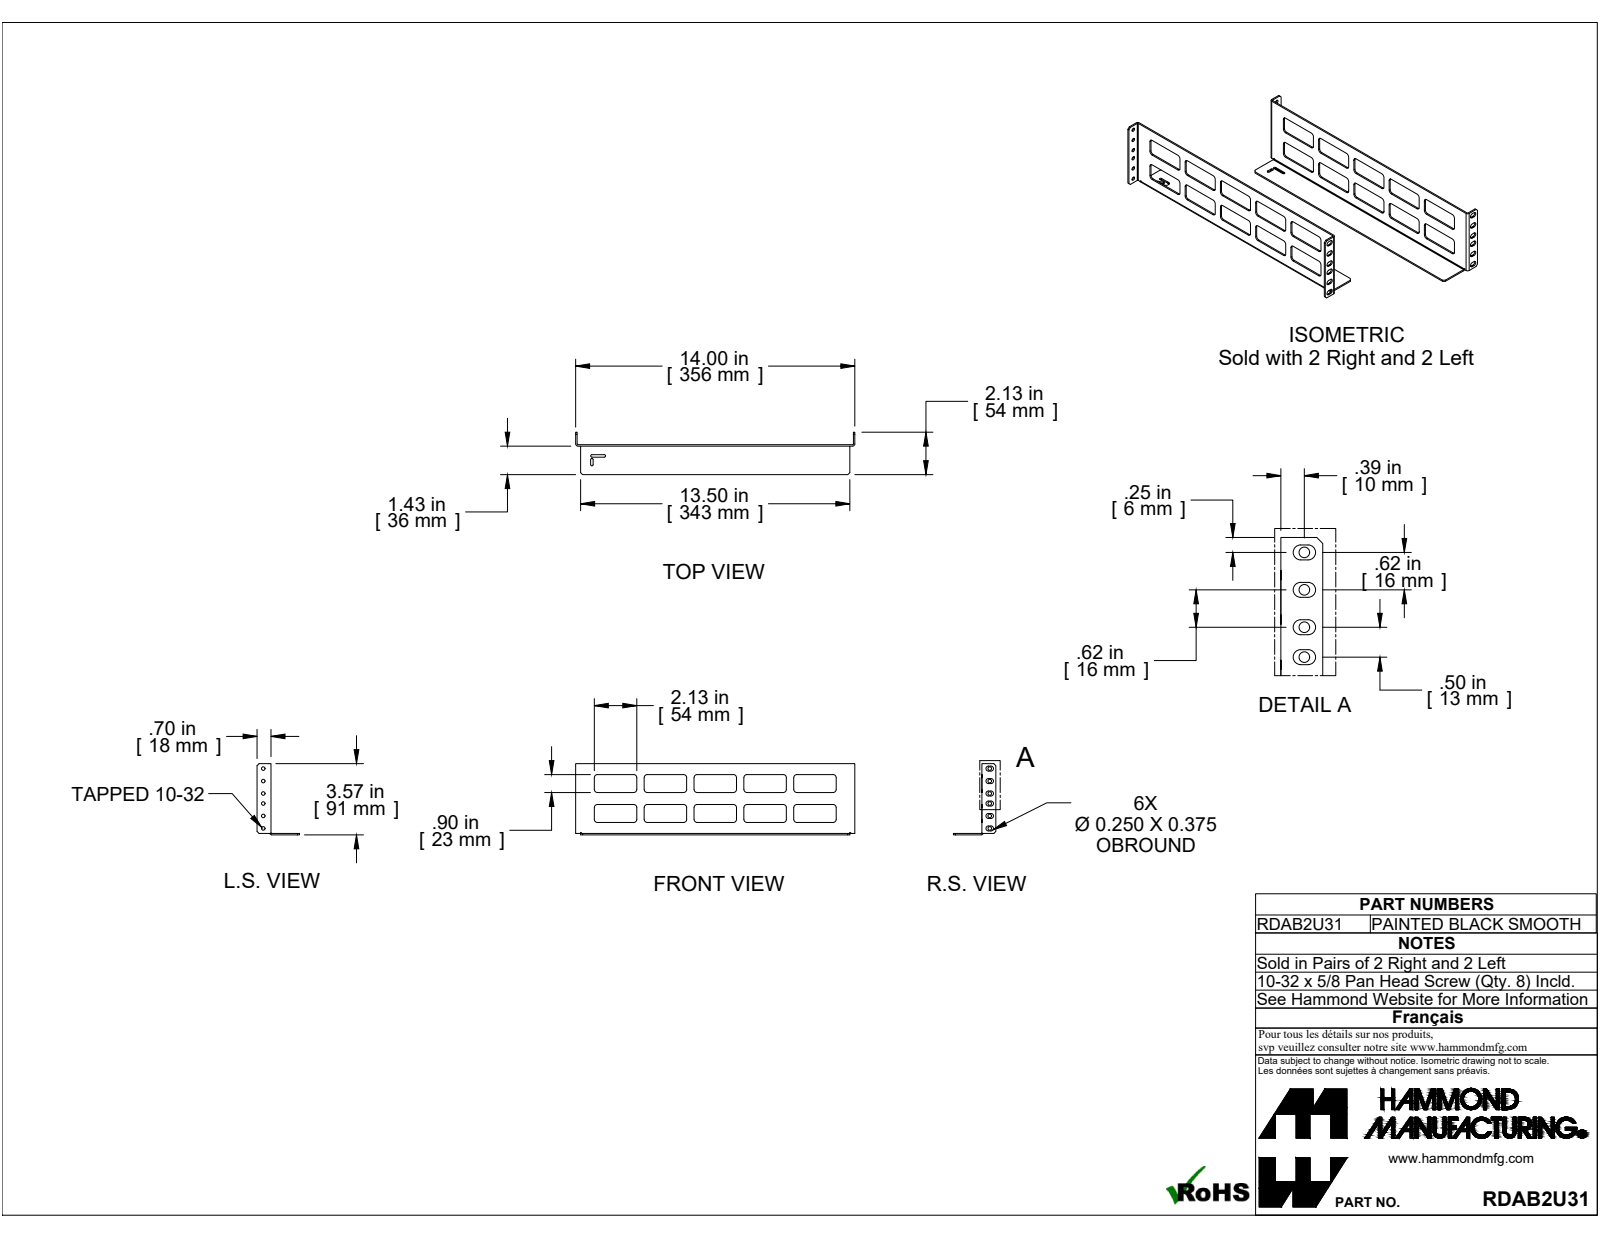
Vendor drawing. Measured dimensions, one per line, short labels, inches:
name: RDAB2U31
written by: SolidWorks 2019 (CONFIG_CONTROL_DESIGN)
unit: in
bodies: 4 solids, 604 faces (328 planar, 276 cylindrical, 0 other)
size: 31 × 18.928 × 3.572
volume: 15.33 in³; area: 457.6 in²
holes: 13× ⌀0.177
rounds: 80× R0.157, 26× R0.125, 10× R0.036, 10× R0.062, 10× R0.108, 4× R0.063, 2× R0.156
face distances: 0.072, 17.6, 17.528, 17.672, 17, 13.928, 1.5, 30.928, 14, 16.928
hole spacings: 18.323, 18.312, 18.396, 1.75, 0.625, 0.625, 18.347, 1.25
